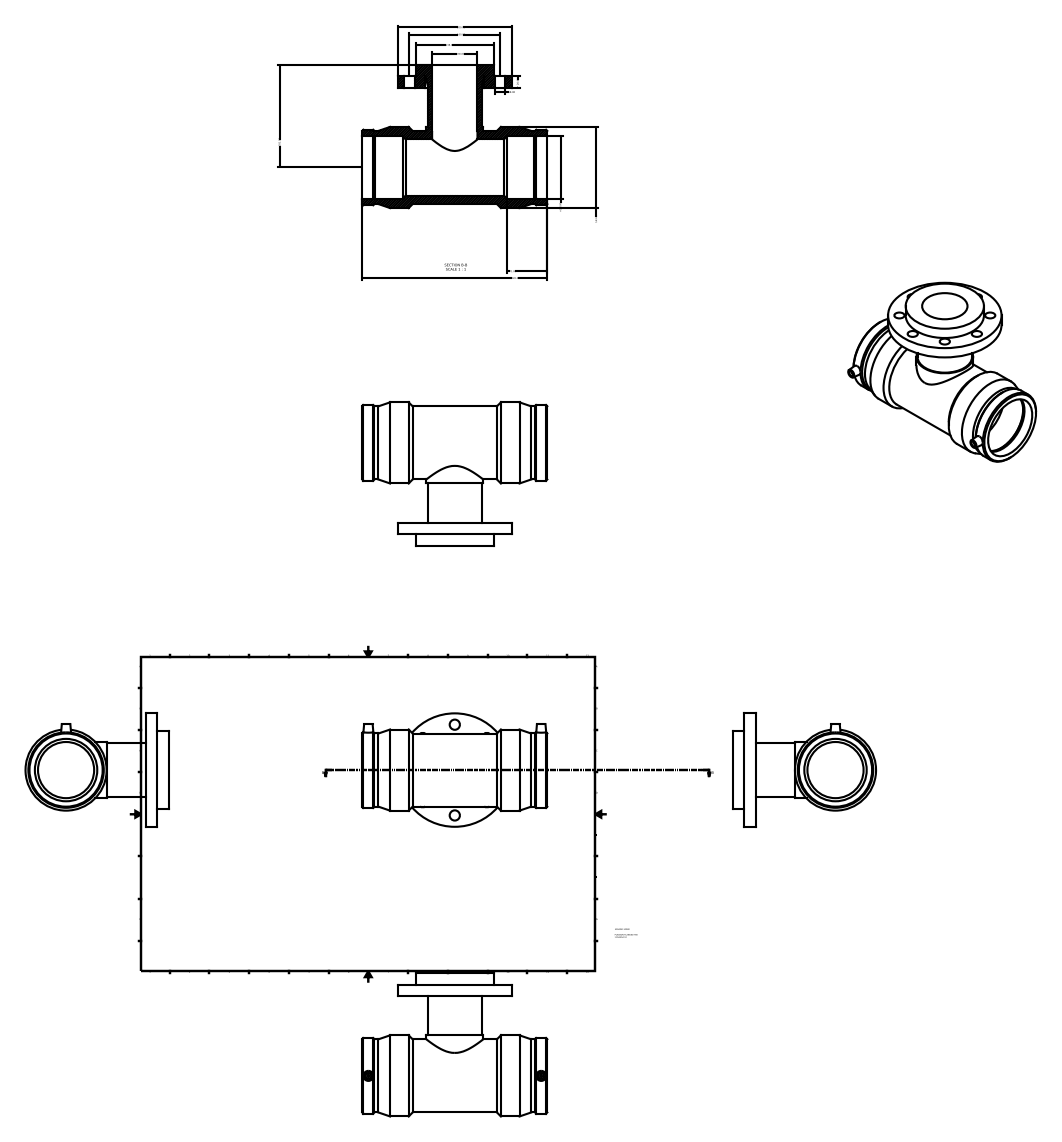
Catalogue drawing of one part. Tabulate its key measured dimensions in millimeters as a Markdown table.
| quantity | value |
| --- | --- |
| part name | 499404110080 |
| STEP written by | Autodesk Inventor 2015 (AUTOMOTIVE_DESIGN) |
| units | millimeters |
| bodies | 1 solid, 64 faces (14 planar, 34 cylindrical, 16 other) |
| overall size | 326 × 252.5 × 200 |
| volume | 2 577 000 mm³ |
| surface area | 396 682 mm² |
| round holes (diameter × count) | 18 × 8, 10 × 2, 80 × 1, 99 × 1, 104 × 1, 110 × 1, 132.99 × 1 |
| round bosses / shafts (diameter × count) | 4 × 2, 200 × 1, 143 × 1, 138 × 1, 129 × 1, 128.7 × 1, 100 × 1, 96 × 1 |
| main face-to-face distances | 20, 40, 326, 109.5, 89.5, 69.5, 22.83, 303.17, 280.34, 14 |
| hole center spacings | 61.23, 80, 113.14, 147.82, 160, 304.7 |
